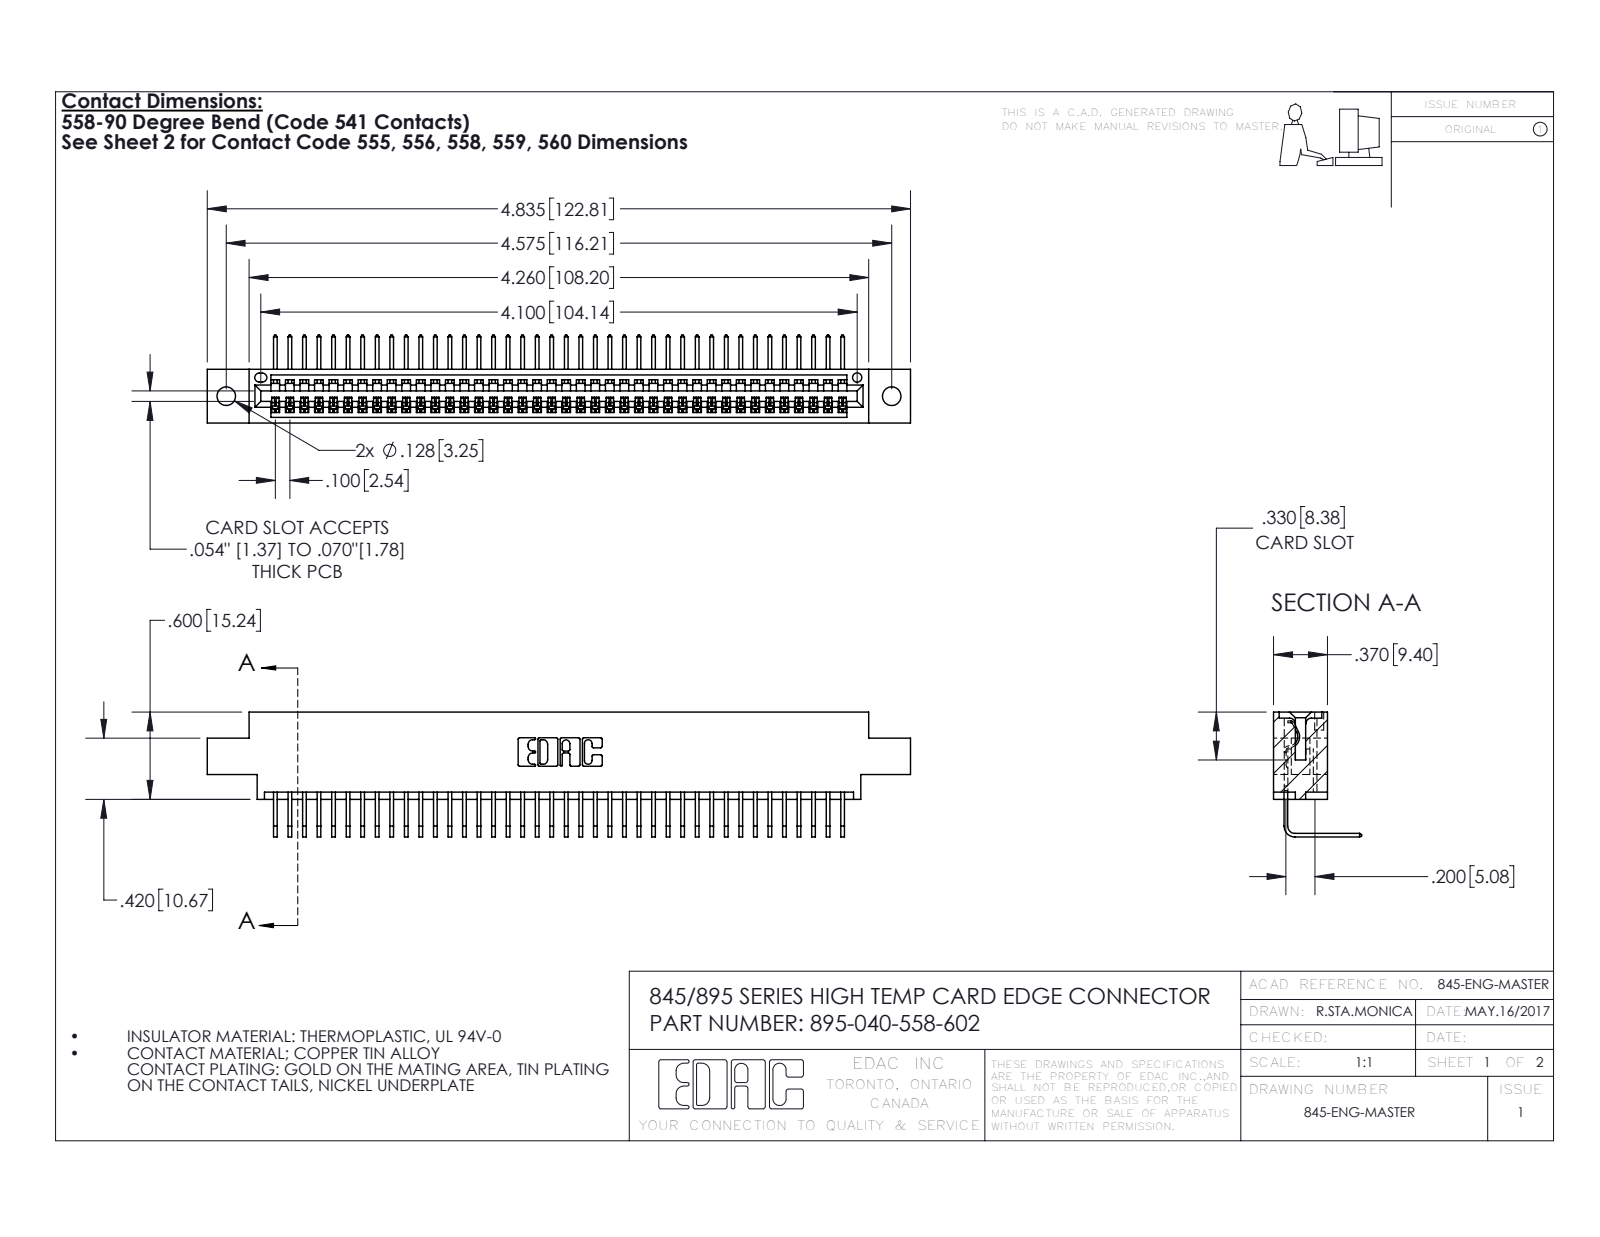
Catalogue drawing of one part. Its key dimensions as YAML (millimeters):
part_name: "345 Part_0.170 Offset - 0.128 Dia; 345-292-001_558 Tail - 2; 395-040-558-602"
step_written_by: "SolidWorks 2016 (CONFIG_CONTROL_DESIGN)"
units: millimeters
bodies: {solids: 41, faces: 2530, planar: 1764, cylindrical: 766, other: 0}
overall_size: [122.8, 21.8, 15.4]
volume: 11600
surface_area: 16070
round_holes:
  - {diameter: 3.3, count: 2}
  - {diameter: 1.6, count: 1}
partial_cylinders:
  - {radius: 0.2, count: 80}
  - {radius: 0.3, count: 22}
  - {radius: 0.2, count: 6}
  - {radius: 0.8, count: 6}
  - {radius: 0.7, count: 3}
  - {radius: 0.8, count: 2}
  - {radius: 1, count: 2}
  - {radius: 0.4, count: 1}
face_to_face_distances: [1.8, 7.6, 9.4, 5.1, 2.5, 6.9, 0.6, 5.7, 4.4, 3.8]
hole_center_spacings: [6.9, 110.2, 116.2]
